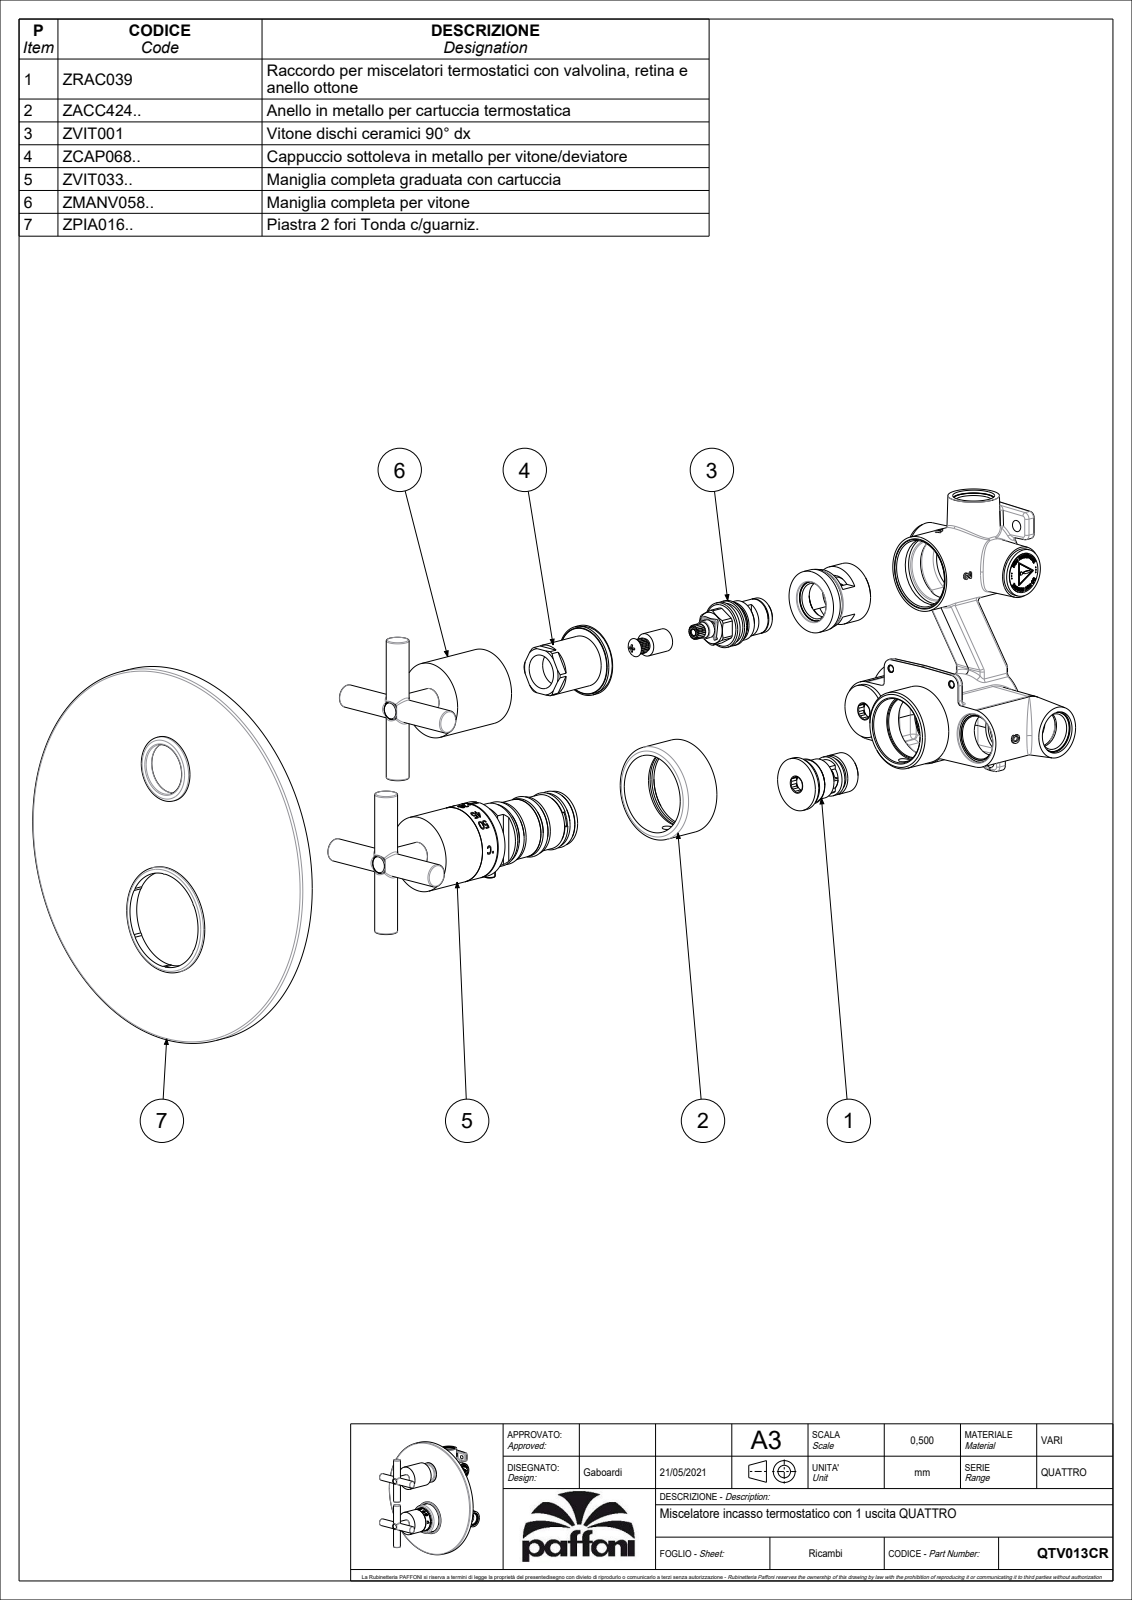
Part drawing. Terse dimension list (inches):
name: QTV013CR
written by: CREO PARAMETRIC BY PTC INC, 2020044 (CONFIG_CONTROL_DESIGN)
unit: in
bodies: 7 solids, 1923 faces (1218 planar, 320 cylindrical, 385 other)
size: 7.874 × 7.874 × 3.748
volume: 16.02 in³; area: 241.6 in²
holes: 2× ⌀0.177, 2× ⌀0.276, 2× ⌀0.315, 2× ⌀1.417, 1× ⌀0.118, 1× ⌀0.13, 1× ⌀0.138, 1× ⌀0.256, 1× ⌀0.354, 1× ⌀0.374, 1× ⌀0.709, 1× ⌀0.787
bosses: 5× ⌀0.472, 2× ⌀1.575, 2× ⌀1.358, 2× ⌀1.102, 2× ⌀1.055, 2× ⌀0.843, 2× ⌀0.551, 2× ⌀0.512
rounds: 30× R0.02, 17× R0.004, 6× R0.062, 4× R0.118, 3× R0.039, 2× R0.012, 2× R0.161, 1× R0.057
face distances: 0.315, 0.276, 0.039, 0.067, 2.449, 0.118, 2.122, 2.516, 2.528, 2.241
hole spacings: 0.197, 1.35, 1.365, 1.878, 3.228, 3.234
